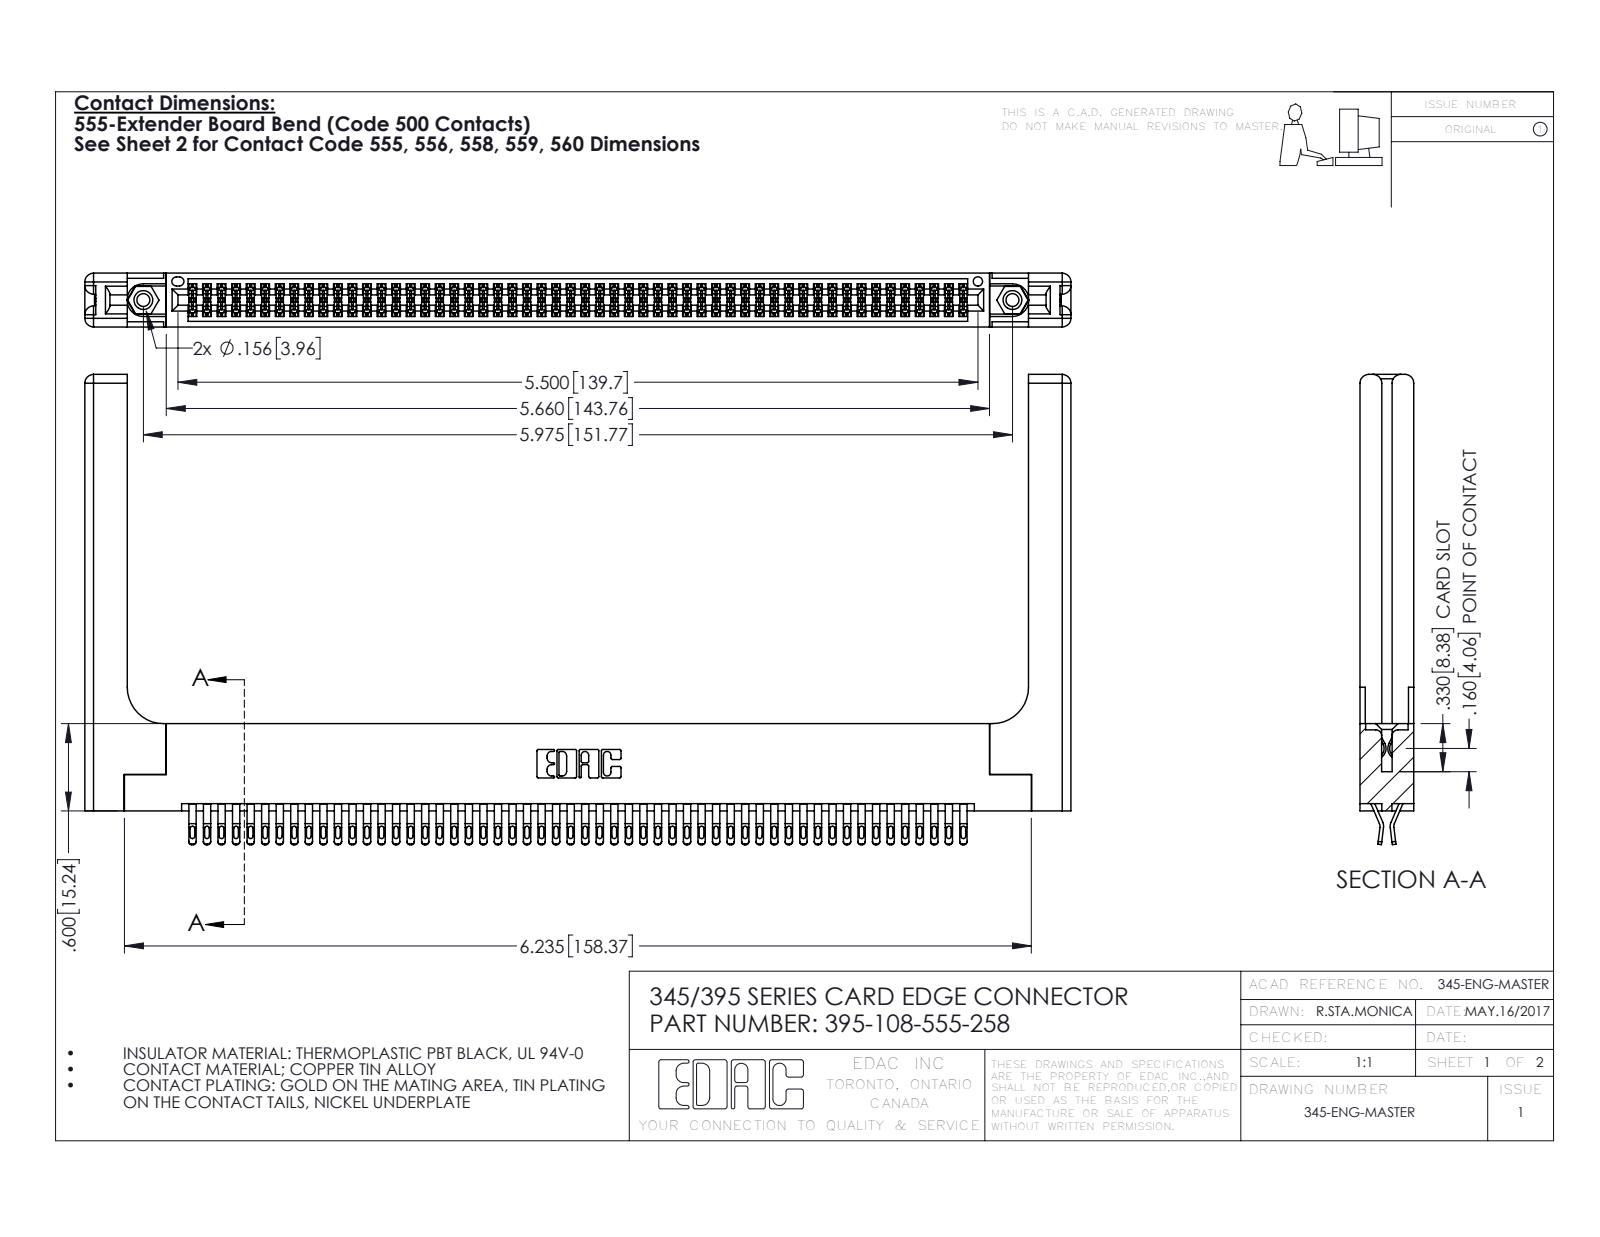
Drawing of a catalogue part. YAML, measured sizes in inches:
part_name: "395-108-555-258; 345-292-001_555 Tail; 345-250-001_345-250-001-102; 345 Part_Flush Mounting Lugs - 0.156 Dia-TH (+1 more)"
step_written_by: "SolidWorks 2016 (CONFIG_CONTROL_DESIGN)"
units: inches
bodies: {solids: 113, faces: 6430, planar: 3576, cylindrical: 2794, other: 60}
overall_size: [6.779, 3.232, 0.37]
volume: 1.564
surface_area: 49.19
round_holes:
  - {diameter: 0.089, count: 2}
  - {diameter: 0.125, count: 2}
  - {diameter: 0.156, count: 2}
  - {diameter: 0.064, count: 1}
round_bosses_or_shafts:
  - {diameter: 0.155, count: 2}
partial_cylinders:
  - {radius: 0.016, count: 270}
  - {radius: 0.02, count: 216}
  - {radius: 0.006, count: 162}
  - {radius: 0.01, count: 22}
  - {radius: 0.06, count: 16}
  - {radius: 0.007, count: 6}
  - {radius: 0.031, count: 6}
  - {radius: 0.026, count: 3}
face_to_face_distances: [0.072, 0.298, 0.37, 0.025, 0.2, 0.098, 0.272, 0.225, 0.148, 0.15]
hole_center_spacings: [0.27, 5.739, 5.975]
